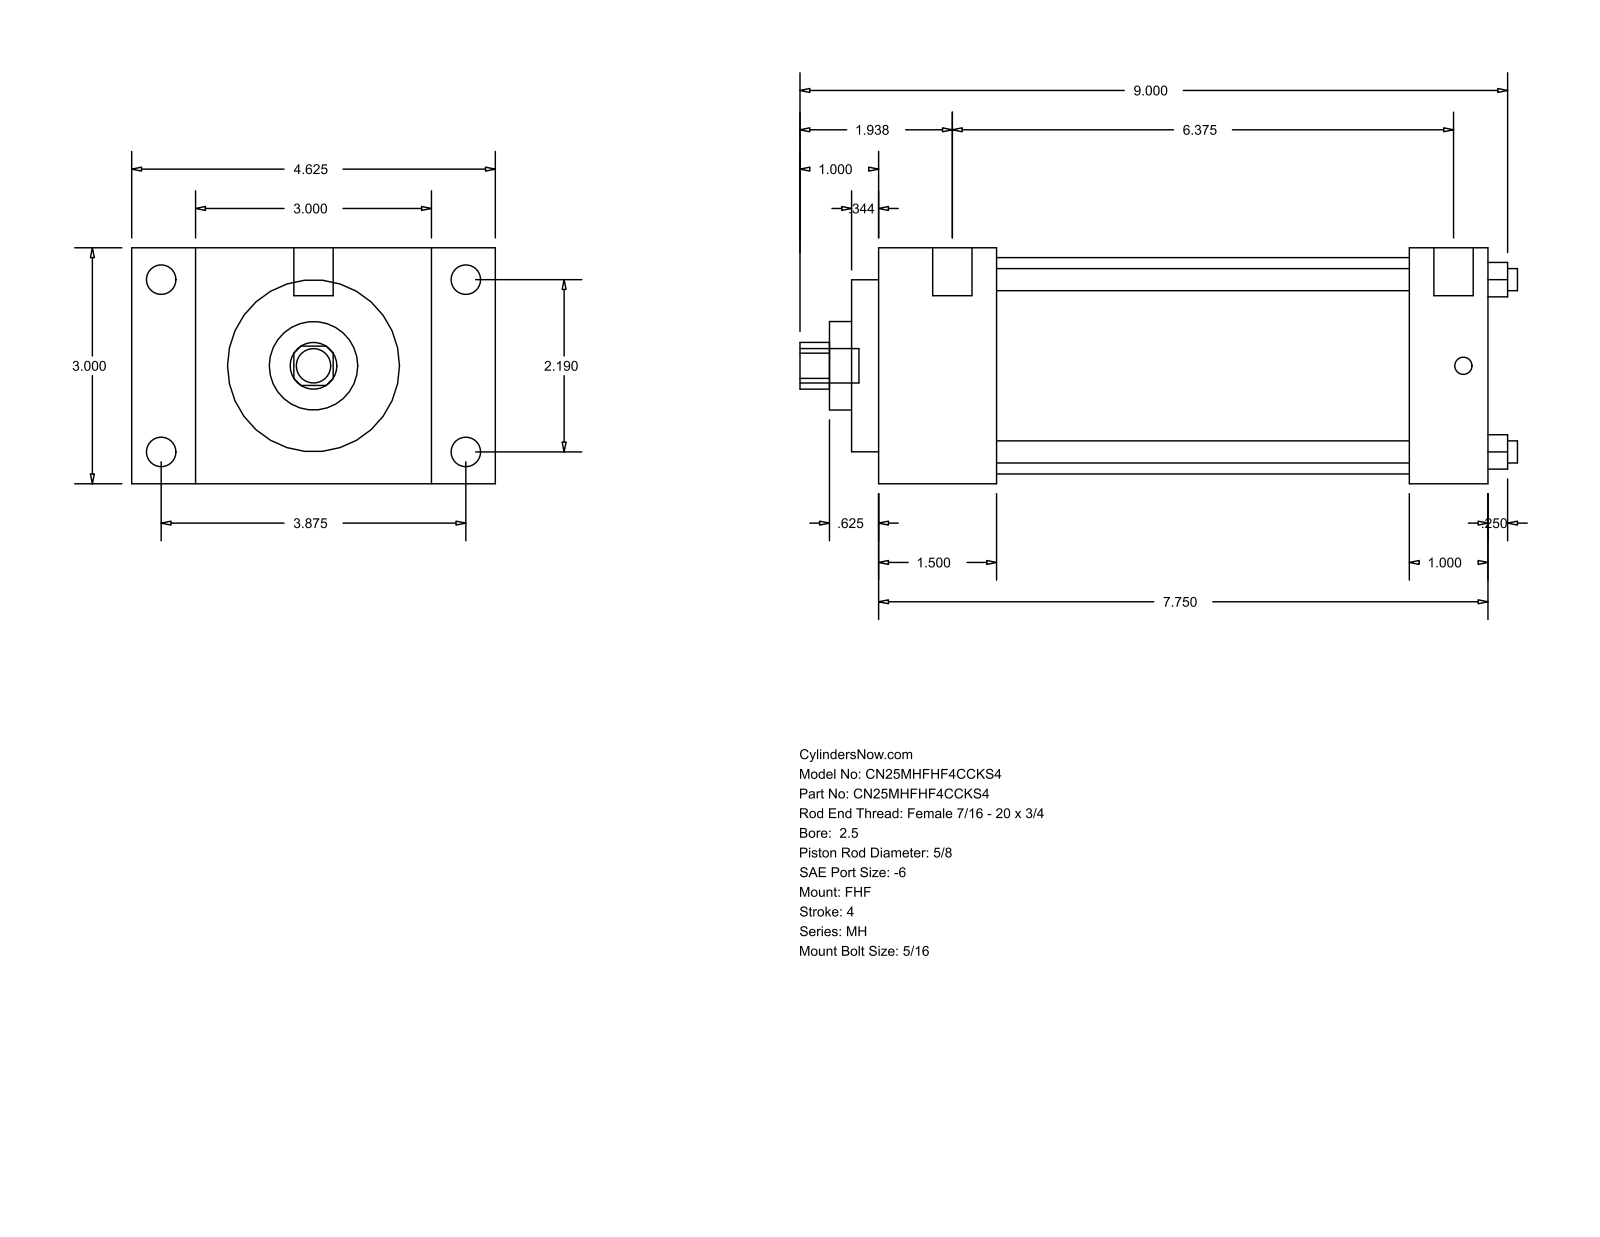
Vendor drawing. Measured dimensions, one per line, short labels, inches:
name: MH_FHF__0250_0.625
written by: GSSL Pune (CONFIG_CONTROL_DESIGN)
unit: in
bodies: 0 solids, 90 faces (61 planar, 29 cylindrical, 0 other)
size: 9.125 × 4.625 × 3
holes: 4× ⌀0.281, 1× ⌀0.625, 1× ⌀1.125, 1× ⌀2.187, 1× ⌀2.75
bosses: 4× ⌀0.375, 4× ⌀0.219, 2× ⌀0.5, 1× ⌀0.437
rounds: 1× R0.297
face distances: 3, 7.75, 1.5, 6.25, 0.813, 3.813, 4.625, 1, 6.75, 5.25
hole spacings: 1.548, 2.19, 3.097
